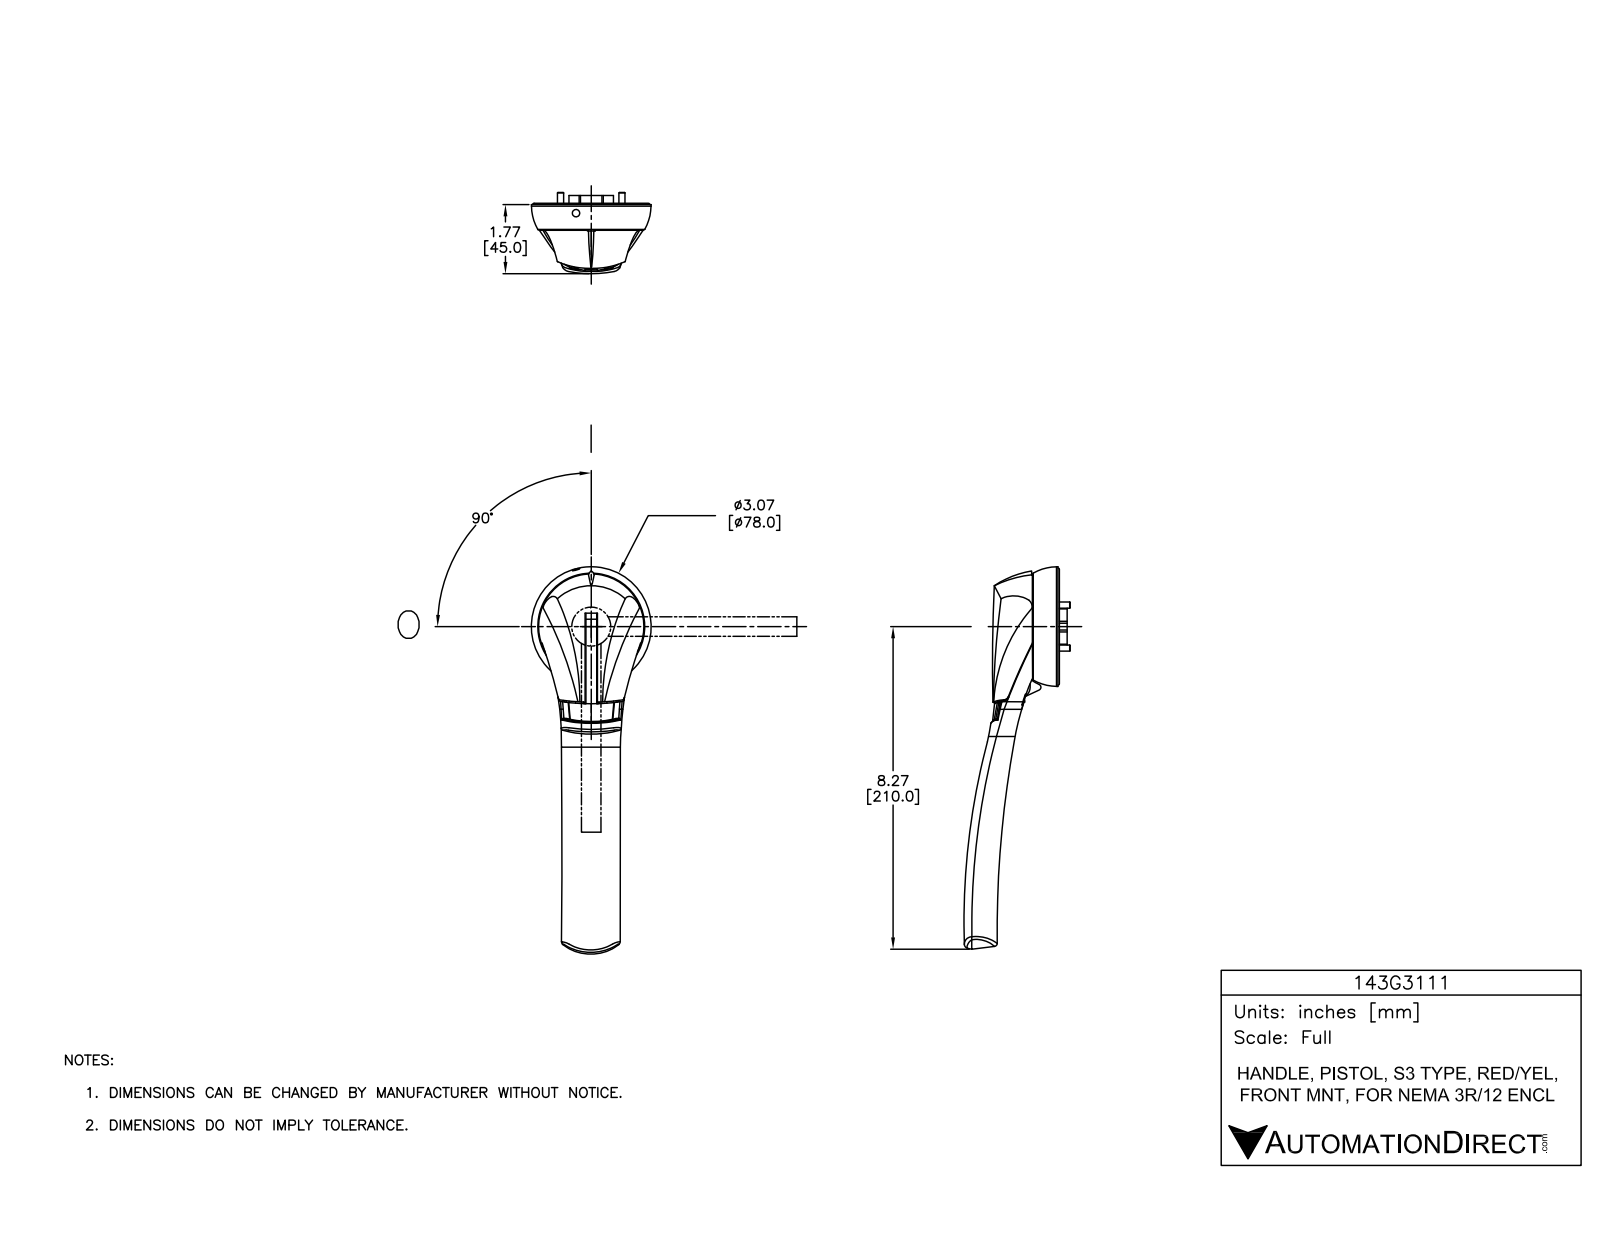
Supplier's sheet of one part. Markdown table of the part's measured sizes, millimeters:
| quantity | value |
| --- | --- |
| part name | 143G3111 |
| STEP written by | SolidWorks 2015 (AUTOMOTIVE_DESIGN) |
| units | millimeters |
| bodies | 8 solids, 1514 faces (806 planar, 544 cylindrical, 164 other) |
| overall size | 248.7 × 78 × 69.1 |
| volume | 211 600 mm³ |
| surface area | 64 770 mm² |
| round holes (diameter × count) | 4 × 6, 8.6 × 4, 10.8 × 4, 0.8 × 3, 4.3 × 2, 9.2 × 2, 3 × 1, 4.8 × 1, 76 × 1 |
| round bosses / shafts (diameter × count) | 0.5 × 11, 8.5 × 4, 8 × 4, 2.3 × 3, 1.8 × 3, 5.8 × 2, 71.6 × 1, 68.6 × 1 |
| partial cylindrical surfaces (radius × count) | 0.3 × 221, 0.4 × 20, 0.9 × 20, 0.8 × 15, 1 × 4, 0.6 × 3, 138.1 × 3, 2 × 2 |
| main face-to-face distances | 0.6, 17.8, 18.1, 17.5, 0.9, 7, 2.6, 4.4, 6.2, 1.2 |
| hole center spacings | 24.4, 7.8, 17, 27.9, 28, 30.6, 40, 47.8 |
